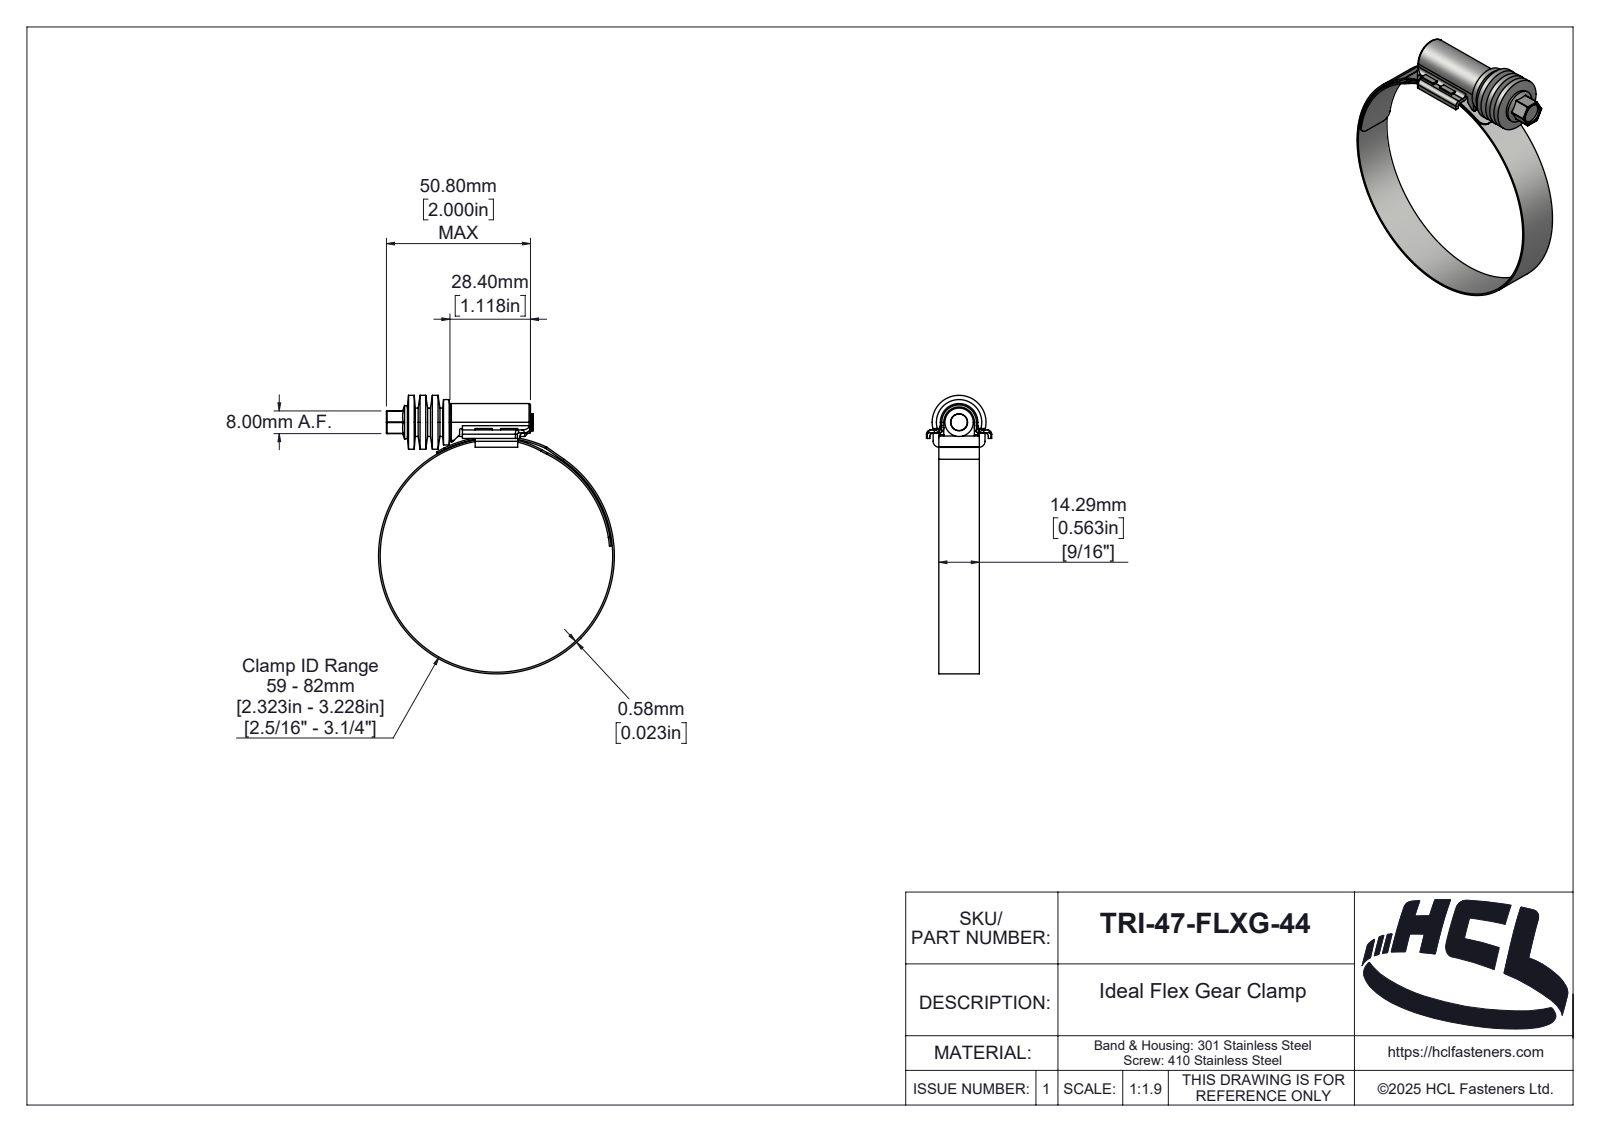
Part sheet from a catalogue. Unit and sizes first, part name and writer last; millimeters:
Units: millimetres
Overall size (bounding box): 98.18 × 83.16 × 23
Round holes (diameter × count): ⌀7 ×1, ⌀82 ×1
Round bosses / shafts (diameter × count): ⌀83.16 ×1, ⌀19 ×1, ⌀16 ×1, ⌀10 ×1, ⌀6 ×1, ⌀5 ×1
Partial cylindrical surfaces — rounded edges, fillets, slot ends (radius × count): R0.2 ×12, R0.5 ×9, R1 ×8, R1.5 ×4, R3 ×4, R2 ×3, R0.1 ×2, R2.1 ×2
Main face-to-face distances: 2, 14.28, 1.2, 4.9, 1.74, 12.54, 16.29, 6.1, 0.58, 0.54
Volume: 10 411 mm³ · Surface area: 16 614 mm²
Bodies: 4 solids, 323 faces (88 planar, 139 cylindrical, 96 other)
Part name (STEP PRODUCT): TRI-47-FLXG-44
STEP written by: SolidWorks 2025 (AUTOMOTIVE_DESIGN)
